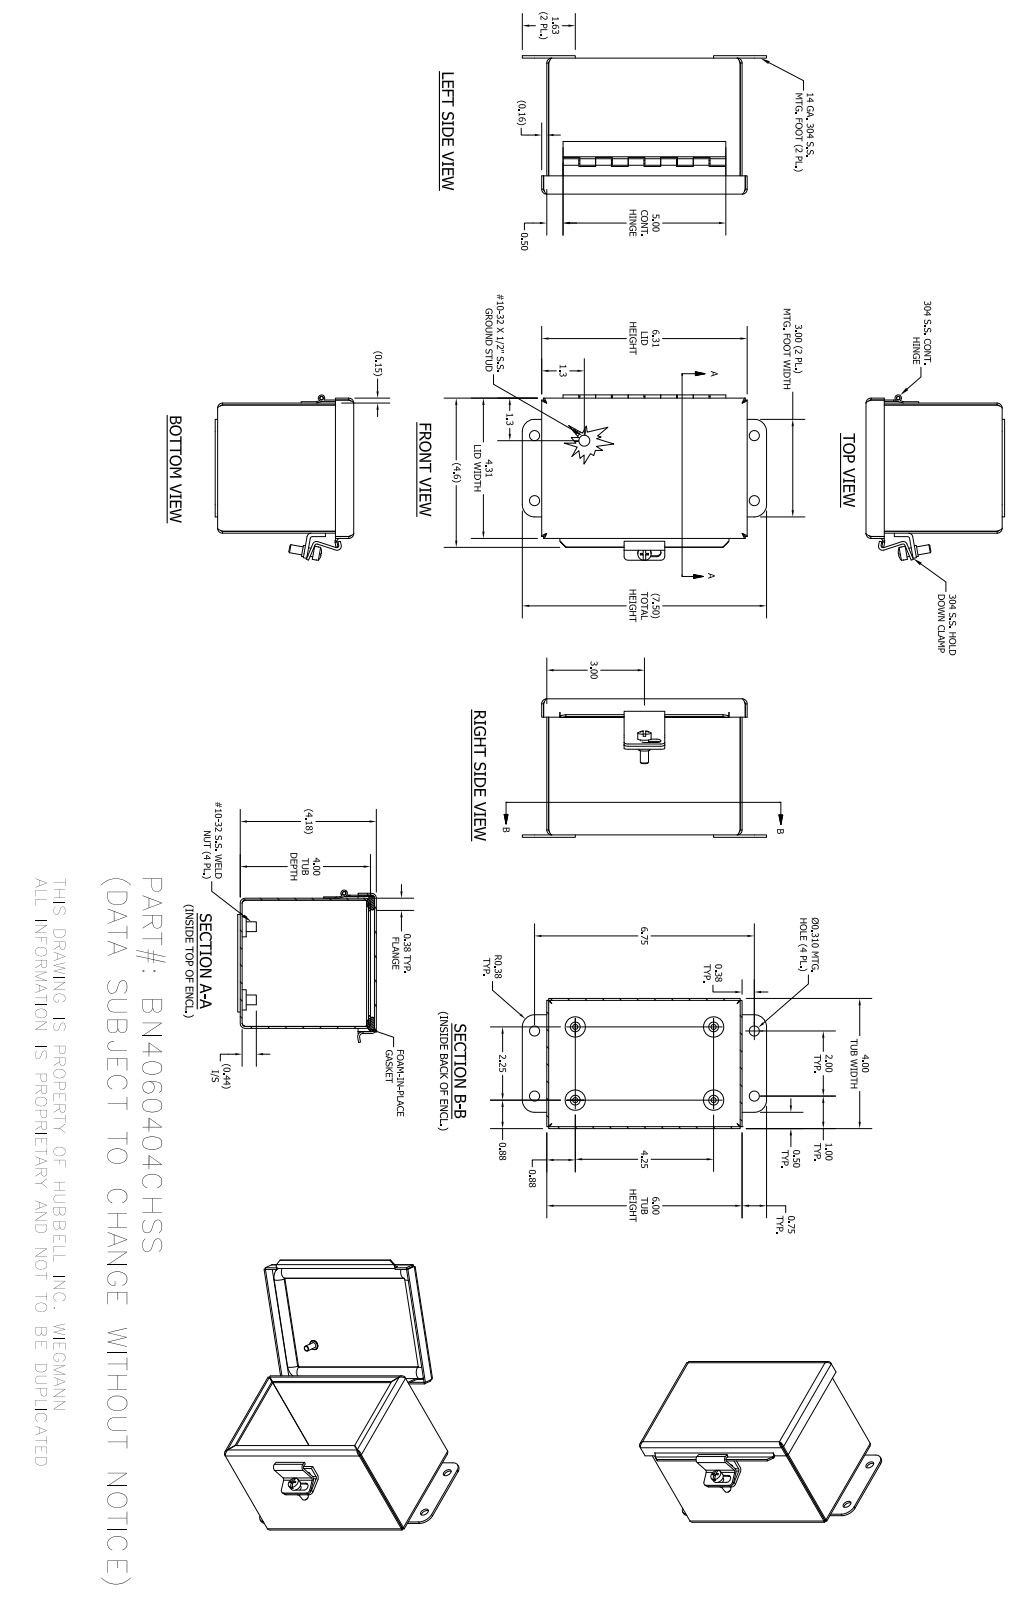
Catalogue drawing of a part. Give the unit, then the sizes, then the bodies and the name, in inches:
Units: inches
Overall size (bounding box): 7.5 × 5.086 × 4.256
Round holes (diameter × count): ⌀0.156 ×4, ⌀0.31 ×4, ⌀0.11 ×2, ⌀0.117 ×1, ⌀0.196 ×1
Round bosses / shafts (diameter × count): ⌀0.625 ×4, ⌀0.3 ×4, ⌀0.409 ×1, ⌀0.344 ×1, ⌀0.337 ×1, ⌀0.25 ×1, ⌀0.2 ×1, ⌀0.19 ×1
Partial cylindrical surfaces — rounded edges, fillets, slot ends (radius × count): R0.094 ×13, R0.153 ×13, R0.066 ×8, R0.125 ×4, R0.228 ×4, R0.375 ×4, R0.063 ×3, R0.126 ×3
Main face-to-face distances: 0.059, 4.122, 3.941, 5.941, 4, 3.882, 4.181, 4.063, 6, 5.882
Hole centre spacings: 1.256, 2.466, 5.501, 5.896, 2, 2.25, 4.25, 4.809
Volume: 11.65 in³ · Surface area: 365.5 in²
Bodies: 16 solids, 343 faces (182 planar, 101 cylindrical, 60 other)
Part name (STEP PRODUCT): B_060404_SSBKP; H4050545LH; H4050545P; H4050545TH (+8 more)
STEP written by: Autodesk Inventor 2016 (AUTOMOTIVE_DESIGN)
